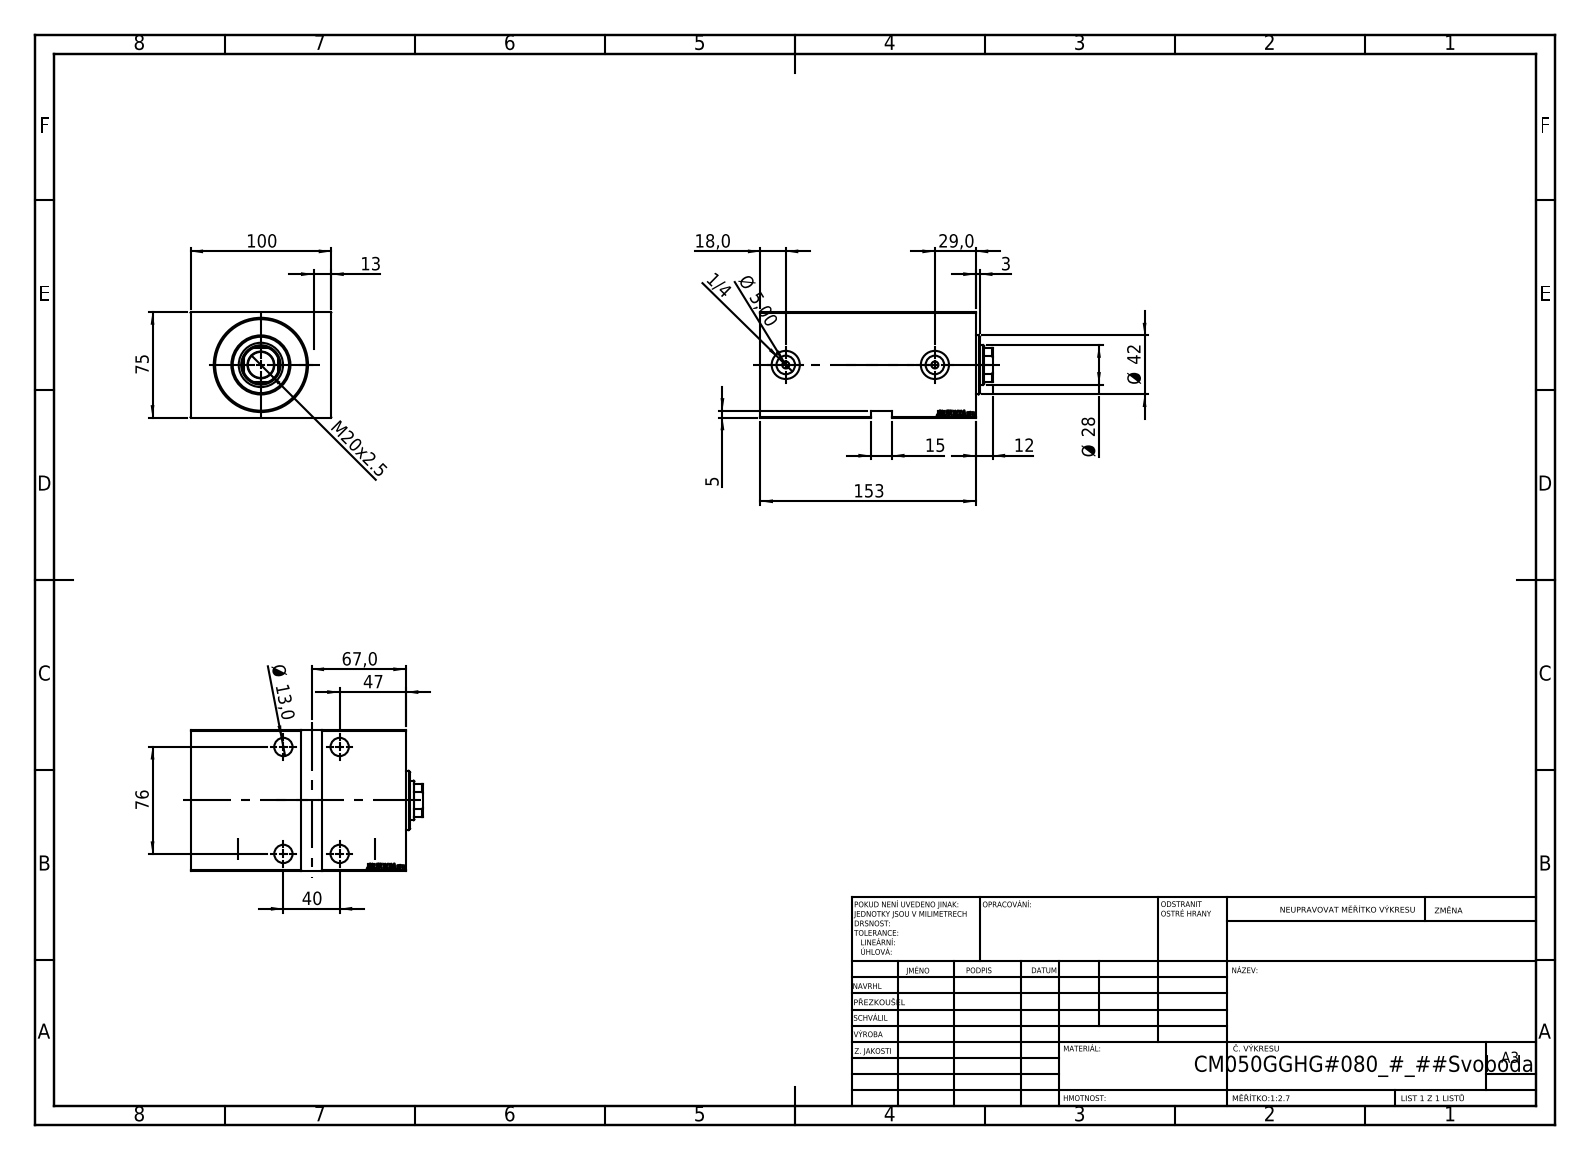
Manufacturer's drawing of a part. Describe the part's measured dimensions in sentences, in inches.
The part is named "Zatka_OIL_PORT; V450CM_G_Body; V450CM_G_VCP; V450CM_VC_G". Its 3-D file was written by "SolidWorks 2019 (CONFIG_CONTROL_DESIGN)". It is 5 solids with 894 faces: 440 planar, 56 cylindrical and 398 other. Overall it measures 6.496 by 3.937 by 2.953 inches. Its volume is 59.09 cubic inches and its surface area 211.8 square inches. Round holes: 4 of diameter 0.512, 4 of diameter 0.748, 2 of diameter 0.197, 2 of diameter 0.518, 2 of diameter 0.787, 1 of diameter 0.728, 1 of diameter 1.102, 1 of diameter 1.24, 1 of diameter 1.969, 1 of diameter 2.047, 1 of diameter 2.559. Round bosses or shafts: 2 of diameter 0.709, 1 of diameter 1.654. Partial cylindrical surfaces (rounded edges, fillets, slot ends): 1 of radius 0.531. The main face-to-face distances are 2.953, 3.937, 6.024, 0.197, 0.551, 5.472, 5.276, 5.827, 2.756, 2.402. The hole center spacings are 1.575, 2.992, 3.381, 4.173.
